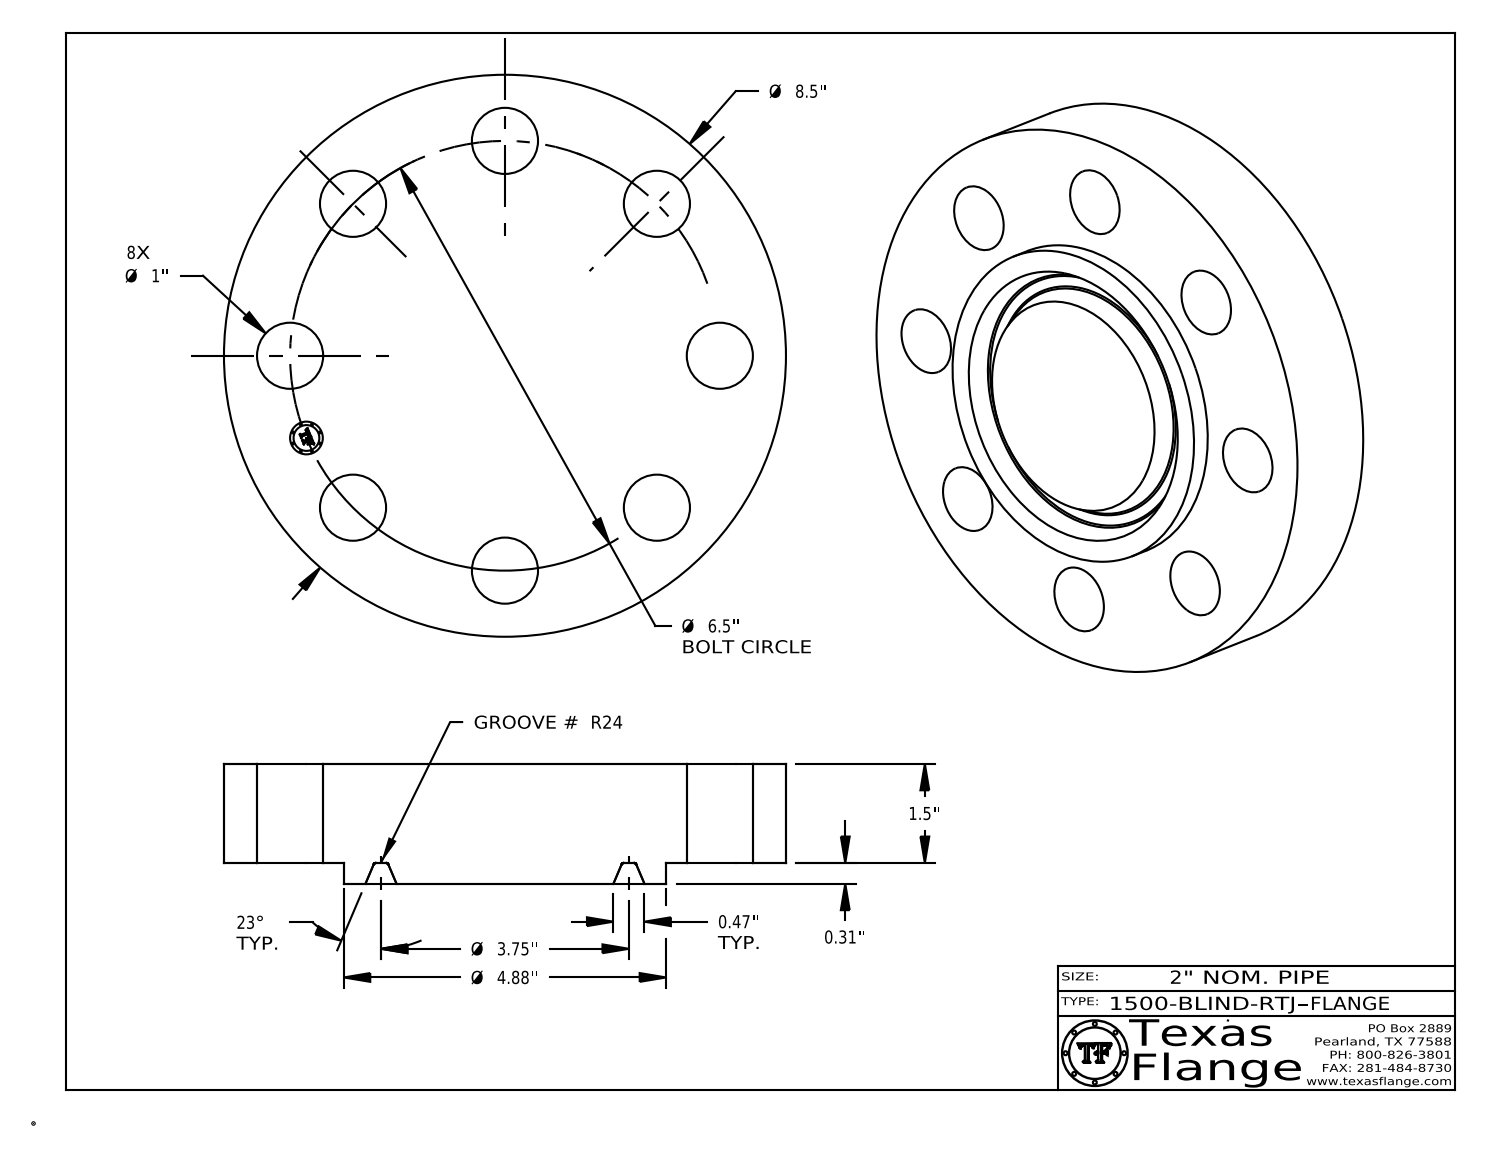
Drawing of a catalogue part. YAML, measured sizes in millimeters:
part_name: "1500-BLIND-RTJ"
step_written_by: "CATIA V5 STEP AP214 (AUTOMOTIVE_DESIGN)"
units: millimeters
bodies: {solids: 1, faces: 418, planar: 370, cylindrical: 40, other: 8}
overall_size: [215.9, 215.9, 46.1]
volume: 1316000
surface_area: 121500
round_holes:
  - {diameter: 25.4, count: 8}
  - {diameter: 12.6, count: 1}
round_bosses_or_shafts:
  - {diameter: 0.8, count: 8}
  - {diameter: 215.9, count: 1}
  - {diameter: 123.8, count: 1}
  - {diameter: 9.9, count: 1}
face_to_face_distances: [38.1, 8, 46.1, 45.7, 37.7, 0.4, 3.8, 3.7, 0.7, 2.4]
hole_center_spacings: [63.2, 116.7, 152.5, 165.1, 32.2, 137.3, 161.9, 91.7]
